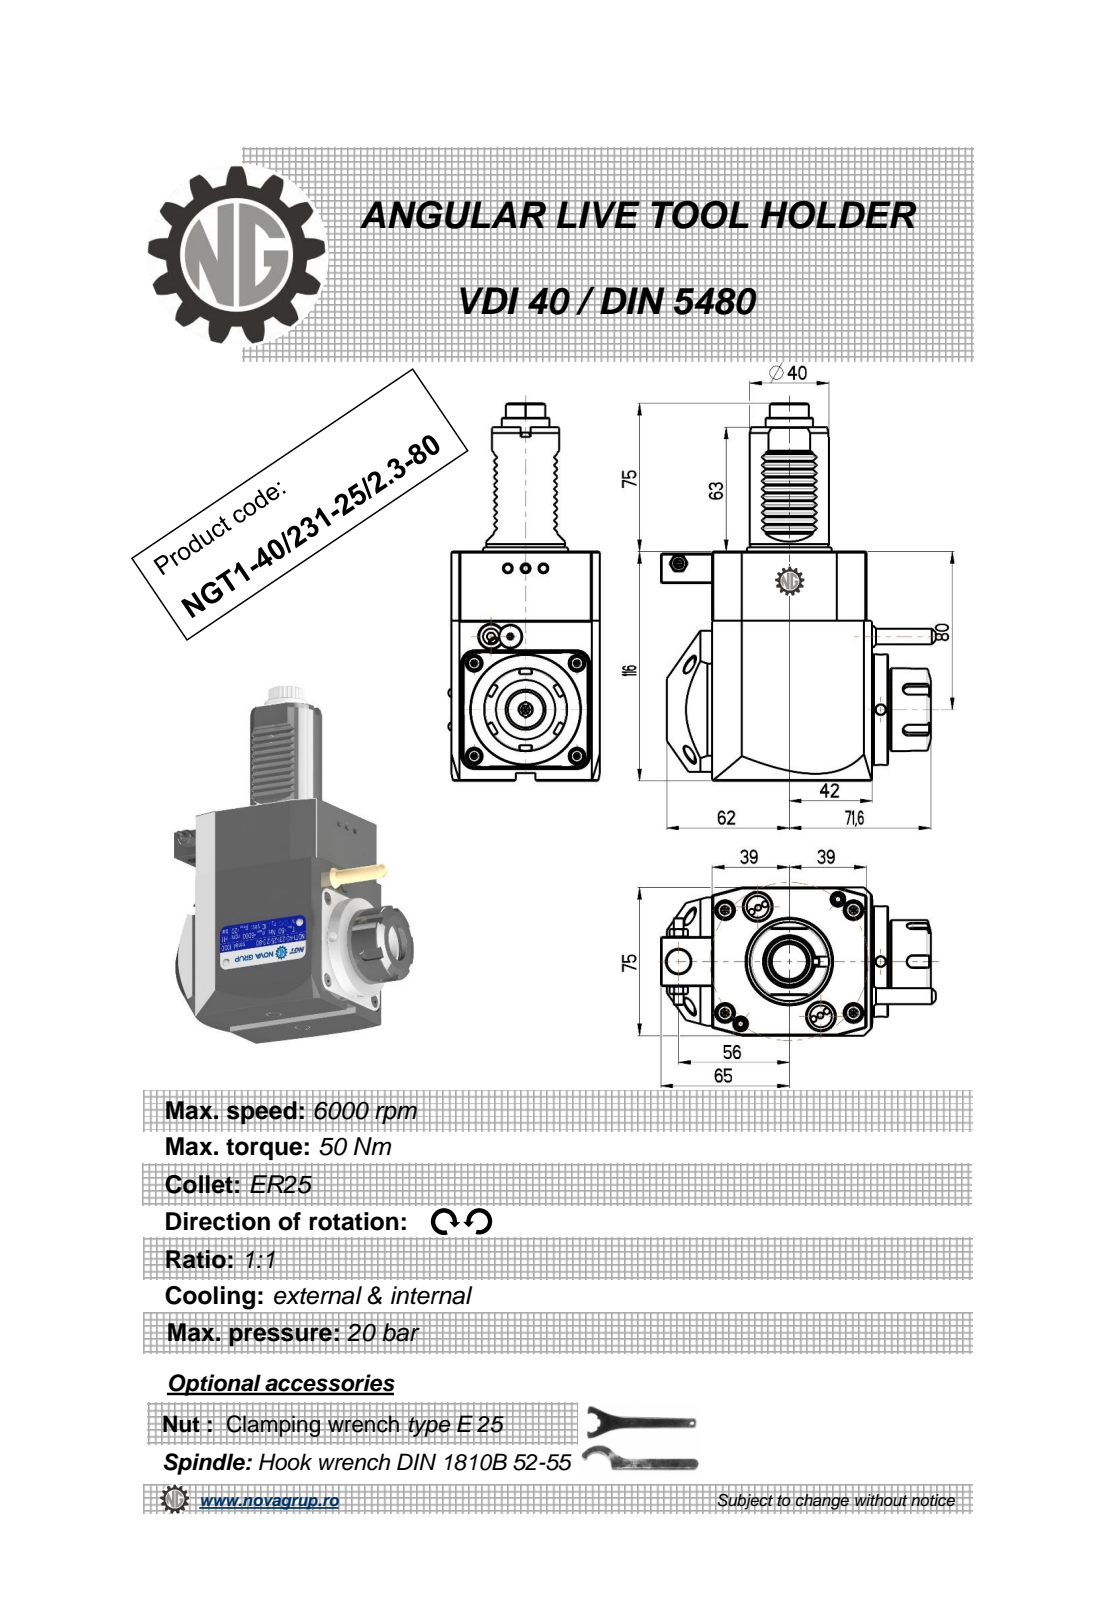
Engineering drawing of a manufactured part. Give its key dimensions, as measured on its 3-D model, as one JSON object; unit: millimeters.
{"part_name": "NGT1_40_231_25_2_3_80", "step_written_by": "PRO/ENGINEER BY PARAMETRIC TECHNOLOGY CORPORATION, 2010280 (CONFIG_CONTROL_DESIGN)", "units": "millimeters", "bodies": {"solids": 1, "faces": 595, "planar": 229, "cylindrical": 191, "other": 175}, "overall_size": [191, 139.14, 75], "volume_mm3": 878089, "surface_area_mm2": 71524, "round_holes": [[5, 3], [3, 1], [4.2, 1], [9.5, 1], [12, 1], [20.3, 1]], "round_bosses_or_shafts": [[56, 1], [43, 1], [42, 1], [40, 1], [33, 1], [24, 1], [11.2, 1], [8.96, 1]], "partial_cylinders_radius": [[2.08, 48], [0.3, 20], [0.26, 12], [0.22, 6], [3, 5], [9.08, 1], [9.92, 1], [15, 1]], "face_to_face_distances": [75, 116, 3, 81, 78, 11, 8, 0.5, 7.5, 80.8], "hole_center_spacings": [38.68, 40.93, 71.5, 102.25, 126.22]}
